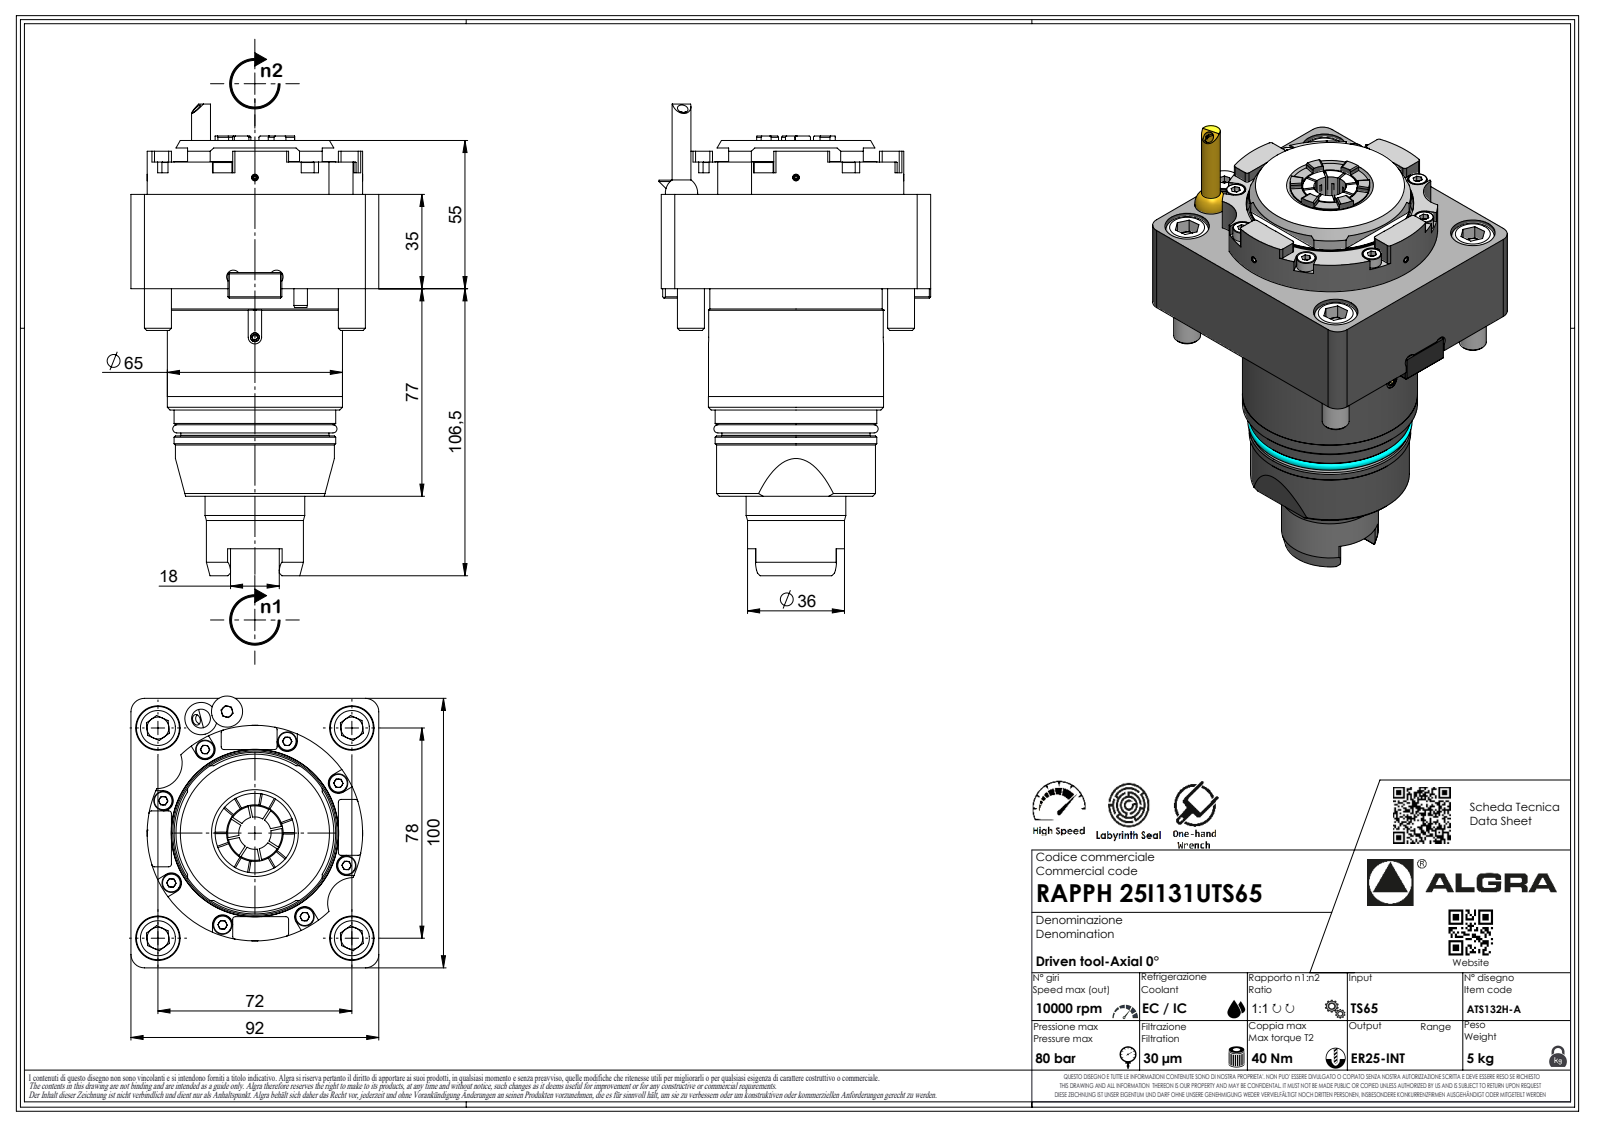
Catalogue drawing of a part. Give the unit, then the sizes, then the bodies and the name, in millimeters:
Units: millimetres
Overall size (bounding box): 175 × 100 × 92
Round holes (diameter × count): ⌀2.1 ×1, ⌀4 ×1
Round bosses / shafts (diameter × count): ⌀10 ×4, ⌀80 ×1, ⌀65 ×1, ⌀64.99 ×1, ⌀64 ×1, ⌀60 ×1, ⌀59 ×1, ⌀55 ×1
Partial cylindrical surfaces — rounded edges, fillets, slot ends (radius × count): R1 ×16, R0.33 ×7, R0.52 ×7, R3.7 ×7, R0.75 ×4, R5 ×4, R9.5 ×2, R0.21 ×1
Main face-to-face distances: 35, 92, 100, 20, 55, 47, 12, 77, 4, 8
Volume: 669 176 mm³ · Surface area: 59 525 mm²
Bodies: 3 solids, 501 faces (320 planar, 77 cylindrical, 104 other)
Part name (STEP PRODUCT): RAPPH25I131UT65
STEP written by: SolidWorks 2023 (AUTOMOTIVE_DESIGN)
